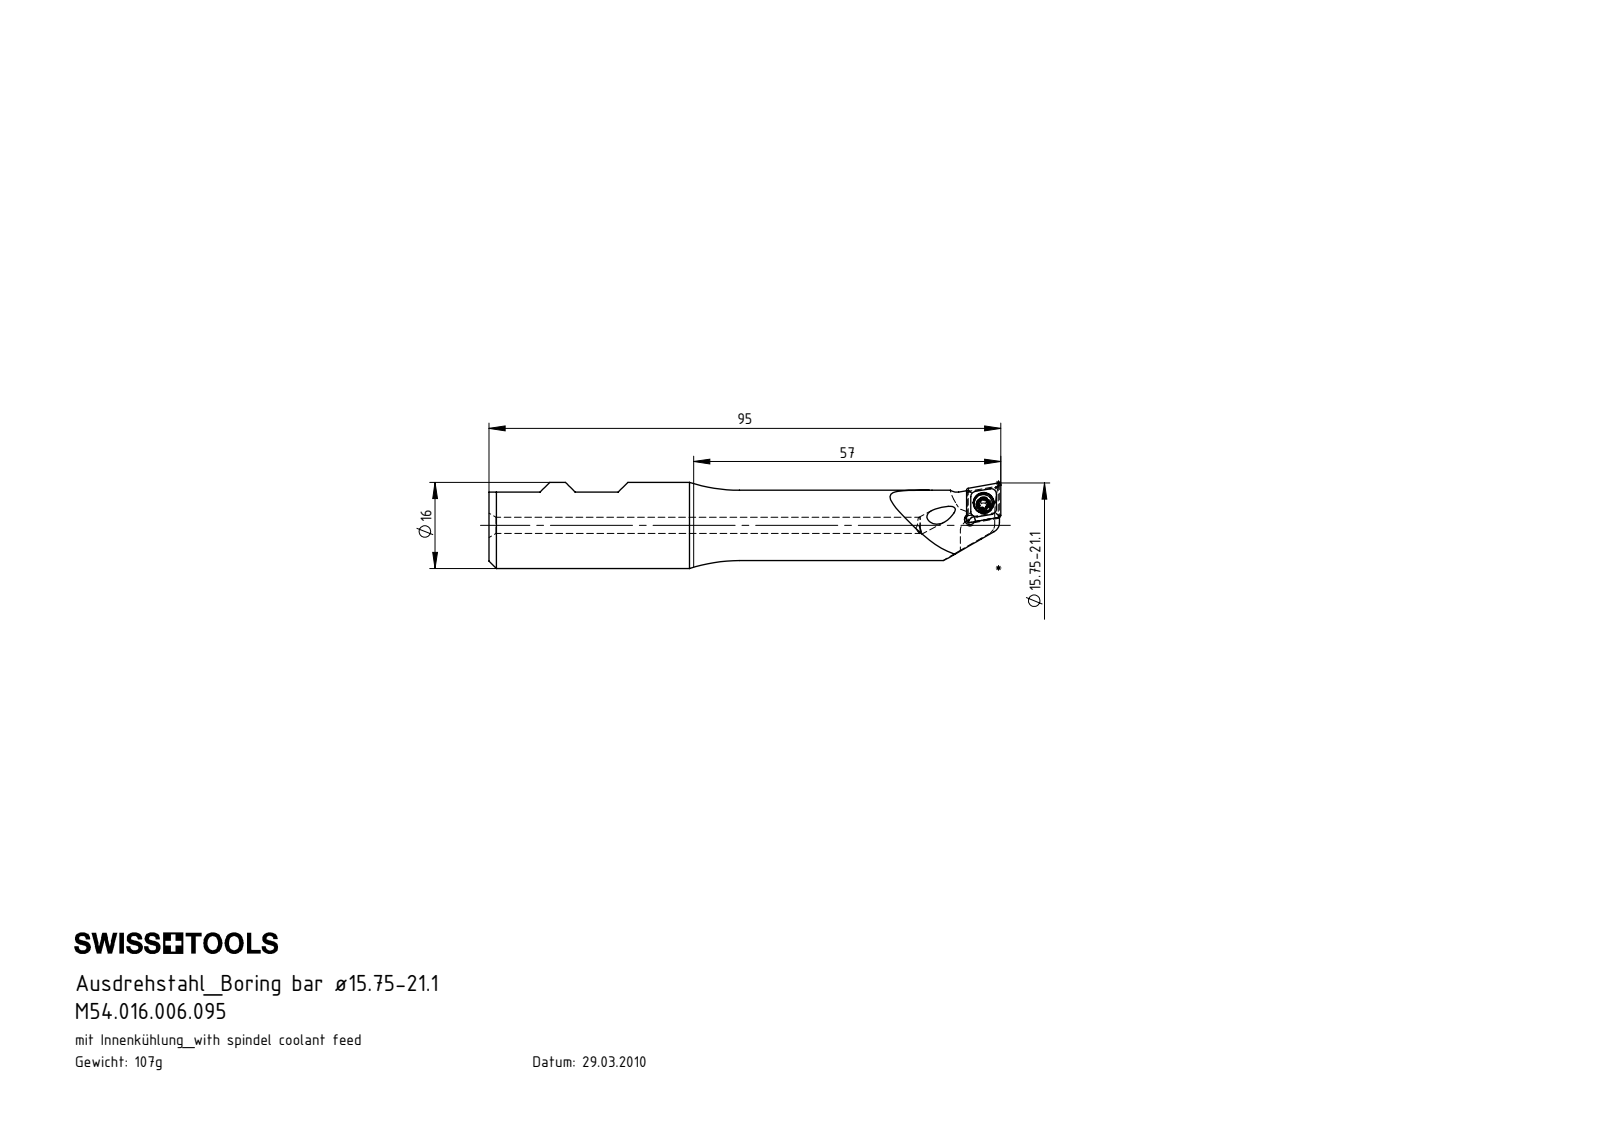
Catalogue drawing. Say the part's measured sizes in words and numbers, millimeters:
The part is named "CCMT060204; B16.WCA.K11.095; B16-WCA.K11.095_A; WCA-ER2.001.006_A". Its 3-D file was written by "SolidWorks 2017 (AUTOMOTIVE_DESIGN)". It is 3 solids with 101 faces: 33 planar, 26 cylindrical and 42 other. Overall it measures 95 by 16 by 16 millimeters. Its volume is 13 562 cubic millimeters and its surface area 5 384 square millimeters. Round holes: 2 of diameter 3, 1 of diameter 2, 1 of diameter 2.05, 1 of diameter 2.8, 1 of diameter 3.85. Round bosses or shafts: 1 of diameter 16, 1 of diameter 13.05, 1 of diameter 3.4, 1 of diameter 2.5. Partial cylindrical surfaces (rounded edges, fillets, slot ends): 6 of radius 0.21, 5 of radius 0.36, 1 of radius 0.36, 1 of radius 2, 1 of radius 6.7, 1 of radius 7.5, 1 of radius 8. The main face-to-face distances are 2.18, 10.25, 5.28, 7.46, 7.66, 2.38, 88.76, 6.76, 1.48, 0.7. The hole center spacings are 3.89, 4.
